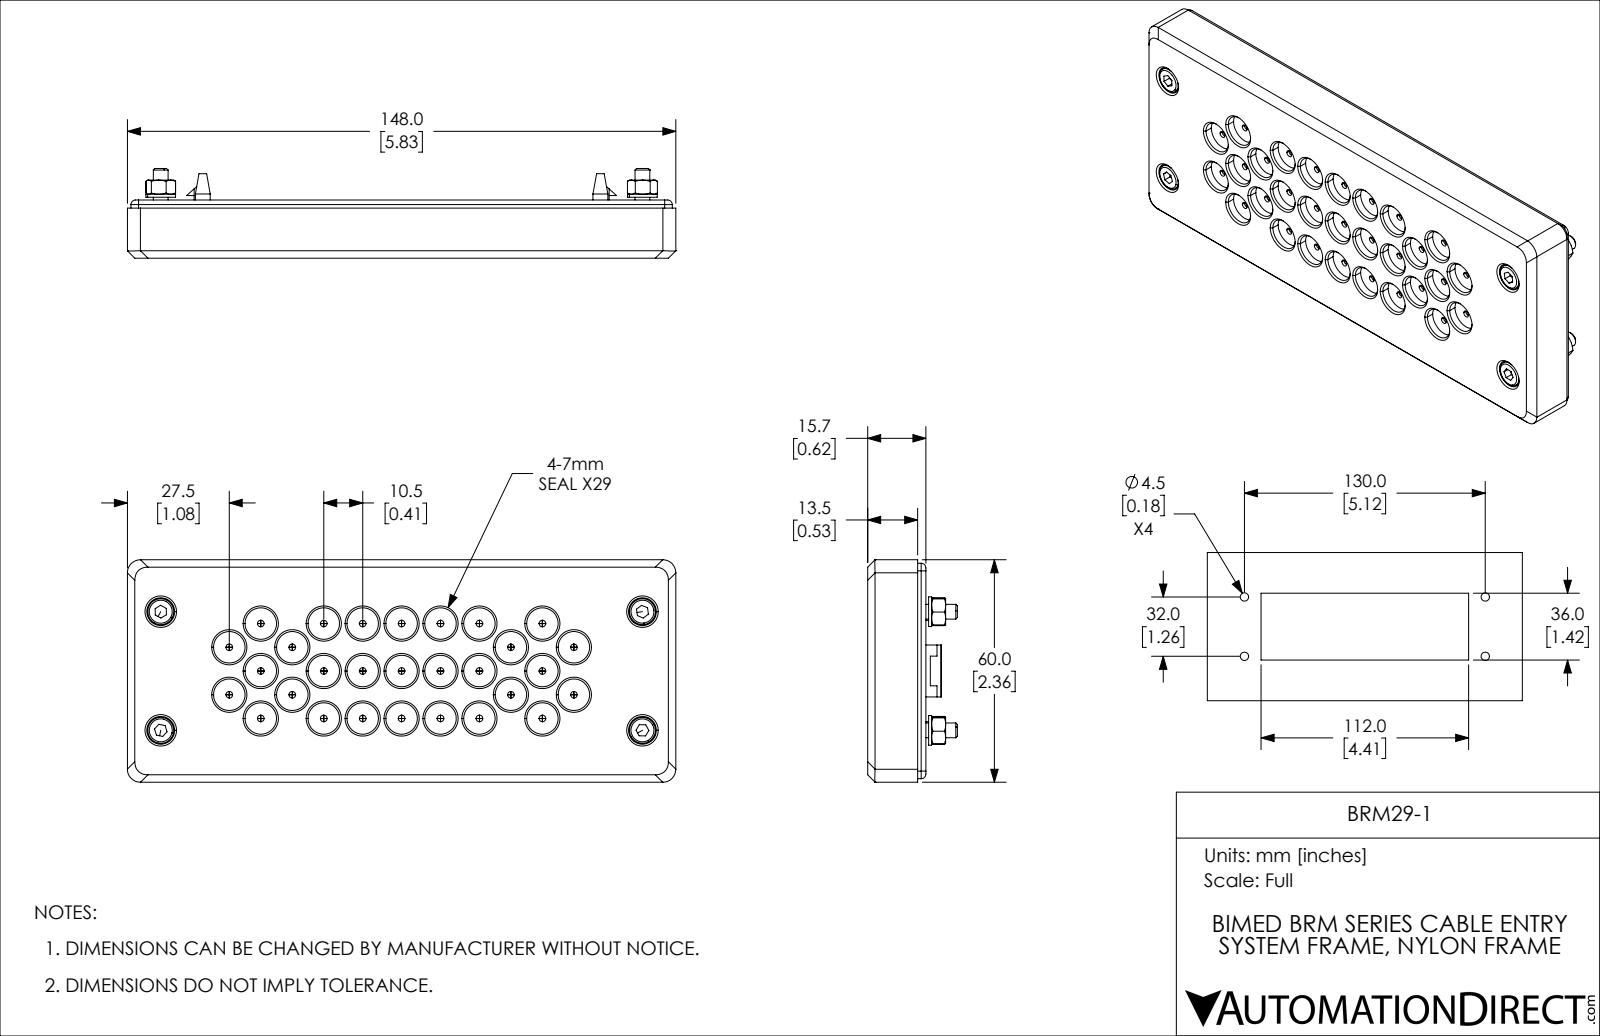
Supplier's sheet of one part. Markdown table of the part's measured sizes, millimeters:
| quantity | value |
| --- | --- |
| part name | BRM29-1 |
| STEP written by | SolidWorks 2021 (CONFIG_CONTROL_DESIGN) |
| units | millimeters |
| bodies | 18 solids, 1649 faces (505 planar, 812 cylindrical, 332 other) |
| overall size | 148 × 60 × 24.2 |
| volume | 90 701 mm³ |
| surface area | 92 298 mm² |
| round holes (diameter × count) | 7.5 × 33, 1.8 × 29, 8.5 × 29, 9.4 × 29, 2.8 × 21, 2.5 × 4, 3.24 × 4, 4.3 × 4, 4.5 × 4 |
| round bosses / shafts (diameter × count) | 2.5 × 16, 4 × 8, 8 × 4, 7 × 4 |
| partial cylindrical surfaces (radius × count) | 3.25 × 29, 1 × 28, 5 × 12, 1.25 × 8, 0.5 × 6, 2 × 4, 2.05 × 4, 3.5 × 4 |
| main face-to-face distances | 0.8, 2, 2.8, 3, 5, 5.8, 2.5, 3.3, 8.3, 5.3 |
| hole center spacings | 10.64, 16.56, 21, 12.8, 10.5, 24.59, 67.8, 21.28 |
